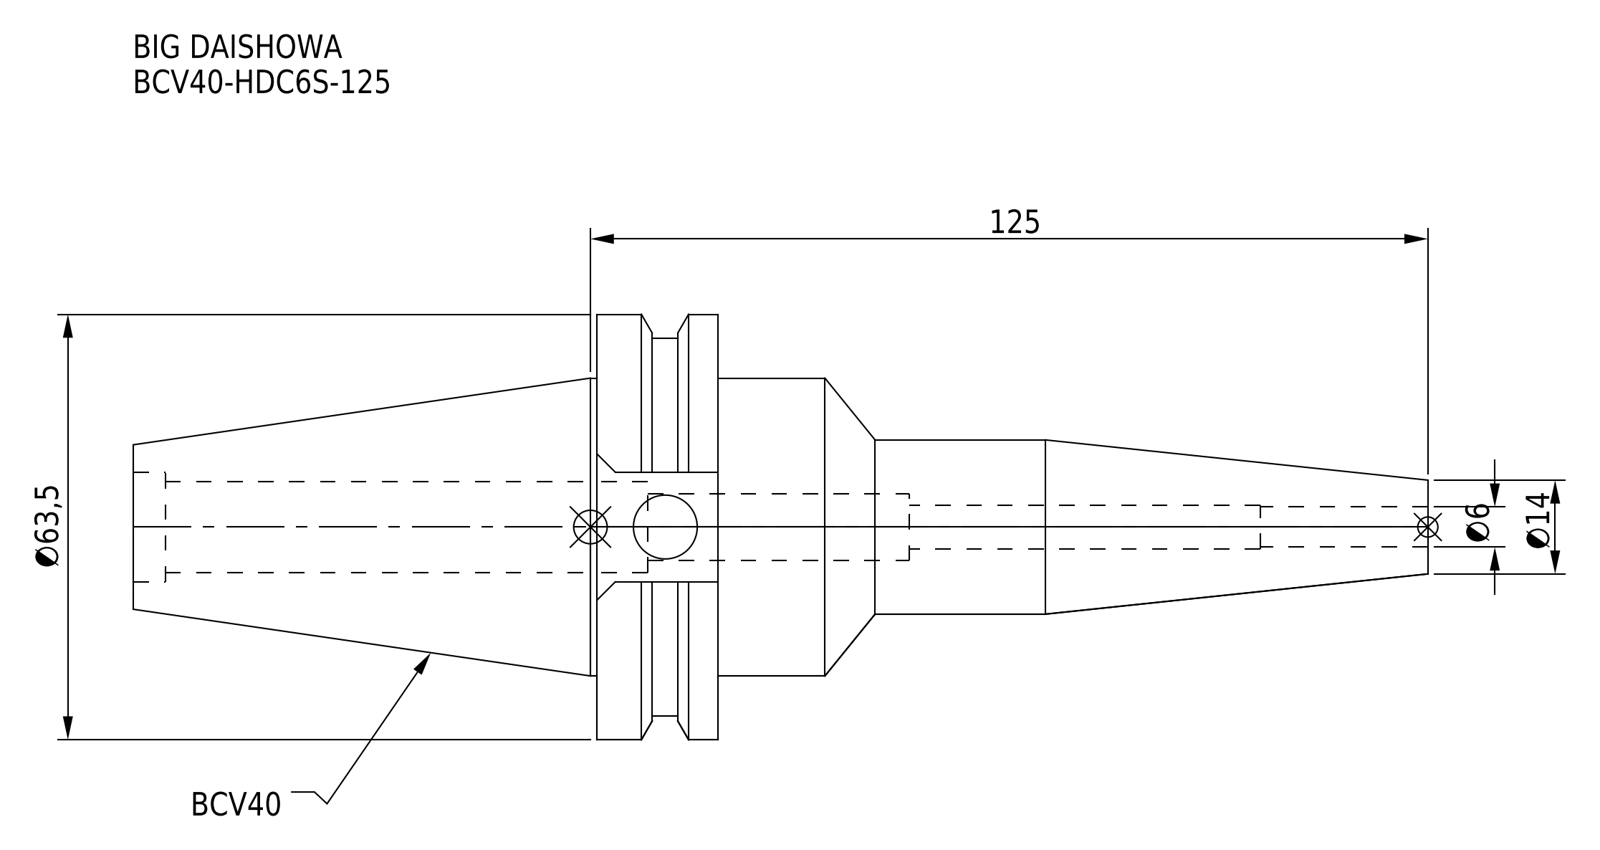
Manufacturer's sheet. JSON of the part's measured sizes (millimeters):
{"part_name": "BCV40-HDC6S-125", "step_written_by": "CREO PARAMETRIC BY PTC INC, 2016380 (AUTOMOTIVE_DESIGN)", "units": "millimeters", "bodies": {"solids": 1, "faces": 59, "planar": 23, "cylindrical": 26, "other": 10}, "overall_size": [193.25, 63.5, 61.35], "volume_mm3": 164015, "surface_area_mm2": 30835, "round_holes": [[6, 1], [6.5, 1], [9.53, 1], [10, 1], [13.6, 1], [16.32, 1]], "round_bosses_or_shafts": [[63.5, 1], [56.36, 1], [44.45, 1], [26, 1]], "face_to_face_distances": [18.05, 87.3, 69.25, 47.55, 16.38, 105.95, 124, 193.25, 111.95, 6]}
